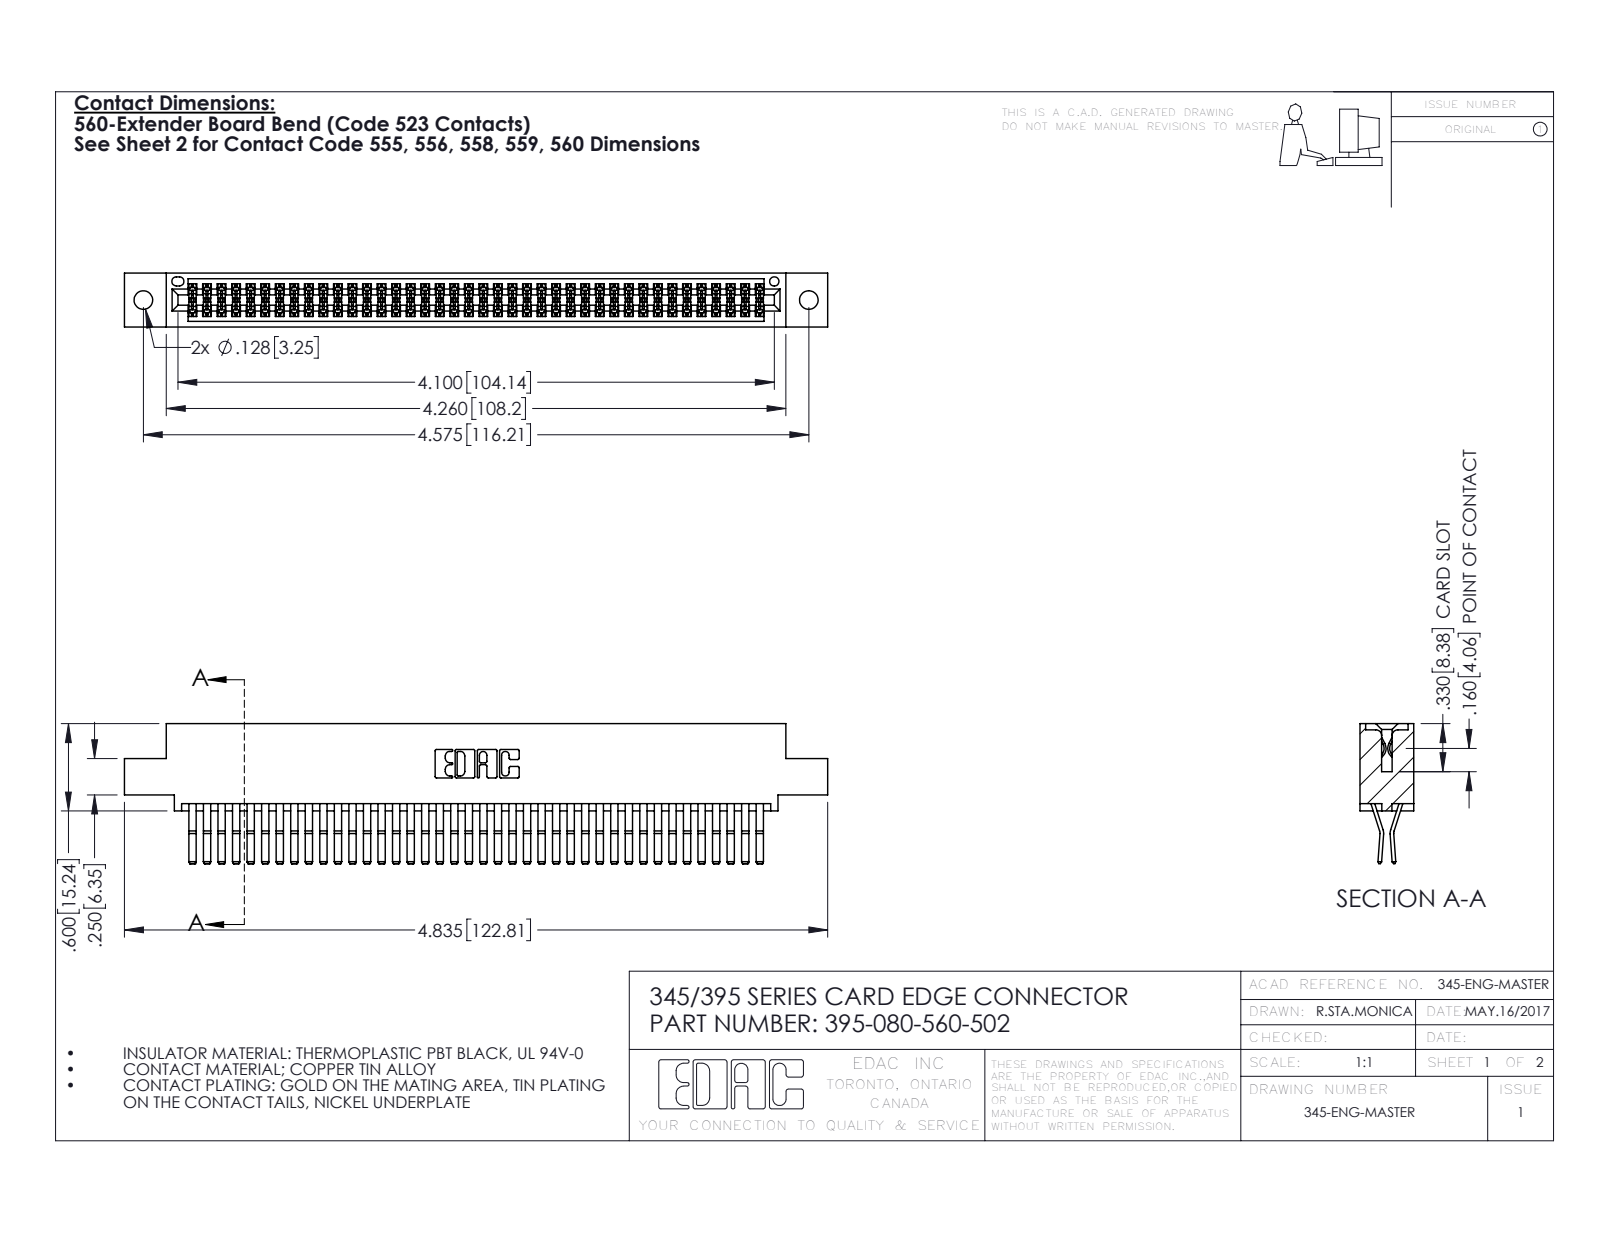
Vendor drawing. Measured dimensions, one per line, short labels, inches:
name: 395-080-560-502; 345 Part_0.110 Offset - 0.128 Dia; 345-292-001_560 Tail
written by: SolidWorks 2016 (CONFIG_CONTROL_DESIGN)
unit: in
bodies: 81 solids, 4290 faces (2724 planar, 1566 cylindrical, 0 other)
size: 4.835 × 0.962 × 0.37
volume: 0.752 in³; area: 29.99 in²
holes: 2× ⌀0.128, 1× ⌀0.064
rounds: 120× R0.006, 22× R0.01, 6× R0.007, 6× R0.031, 3× R0.026, 2× R0.01, 2× R0.014, 2× R0.019
face distances: 0.025, 0.298, 0.072, 0.37, 0.2, 0.098, 0.272, 0.225, 0.175, 0.149
hole spacings: 0.27, 4.339, 4.575
